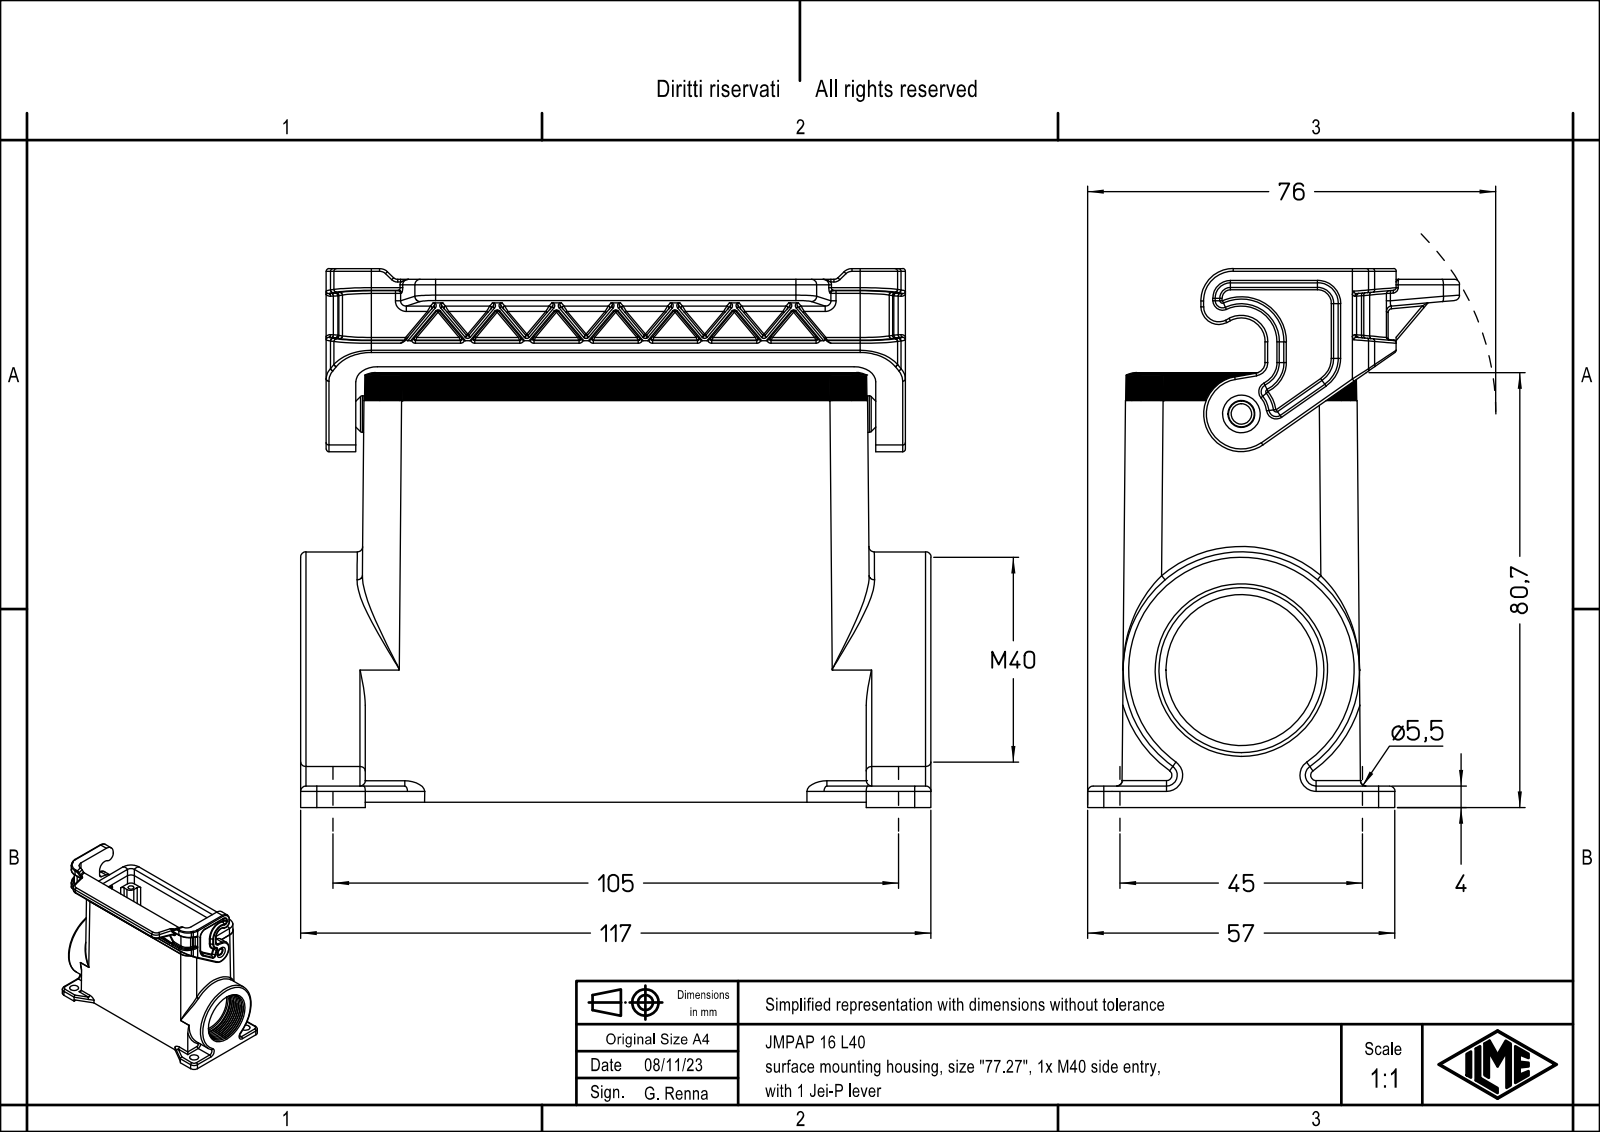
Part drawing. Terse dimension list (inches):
name: JMPAP 16 L40
written by: Creo Elements/Direct Modeling 20.1B 02-Apr-2019 (C) Parametric Technology GmbH (AUTOMOTIVE_DESIGN)
unit: in
bodies: 1 solid, 850 faces (186 planar, 352 cylindrical, 312 other)
size: 4.606 × 3.937 × 2.717
volume: 8.163 in³; area: 102.7 in²
holes: 4× ⌀0.118, 4× ⌀0.138, 3× ⌀0.217, 1× ⌀0.189, 1× ⌀1.315, 1× ⌀1.52
bosses: 1× ⌀1.727, 1× ⌀0.268
rounds: 99× R0.012, 77× R0.02, 23× R0.039, 16× R0.118, 11× R0.079, 9× R0.276, 8× R0.059, 8× R0.157
face distances: 0.118, 0.157, 0.039, 3.858, 3.819, 3.701, 0.276, 0.463, 1.531, 0.404
hole spacings: 0.647, 1.517, 3.61, 3.862, 1.063, 3.051, 3.231, 1.772
